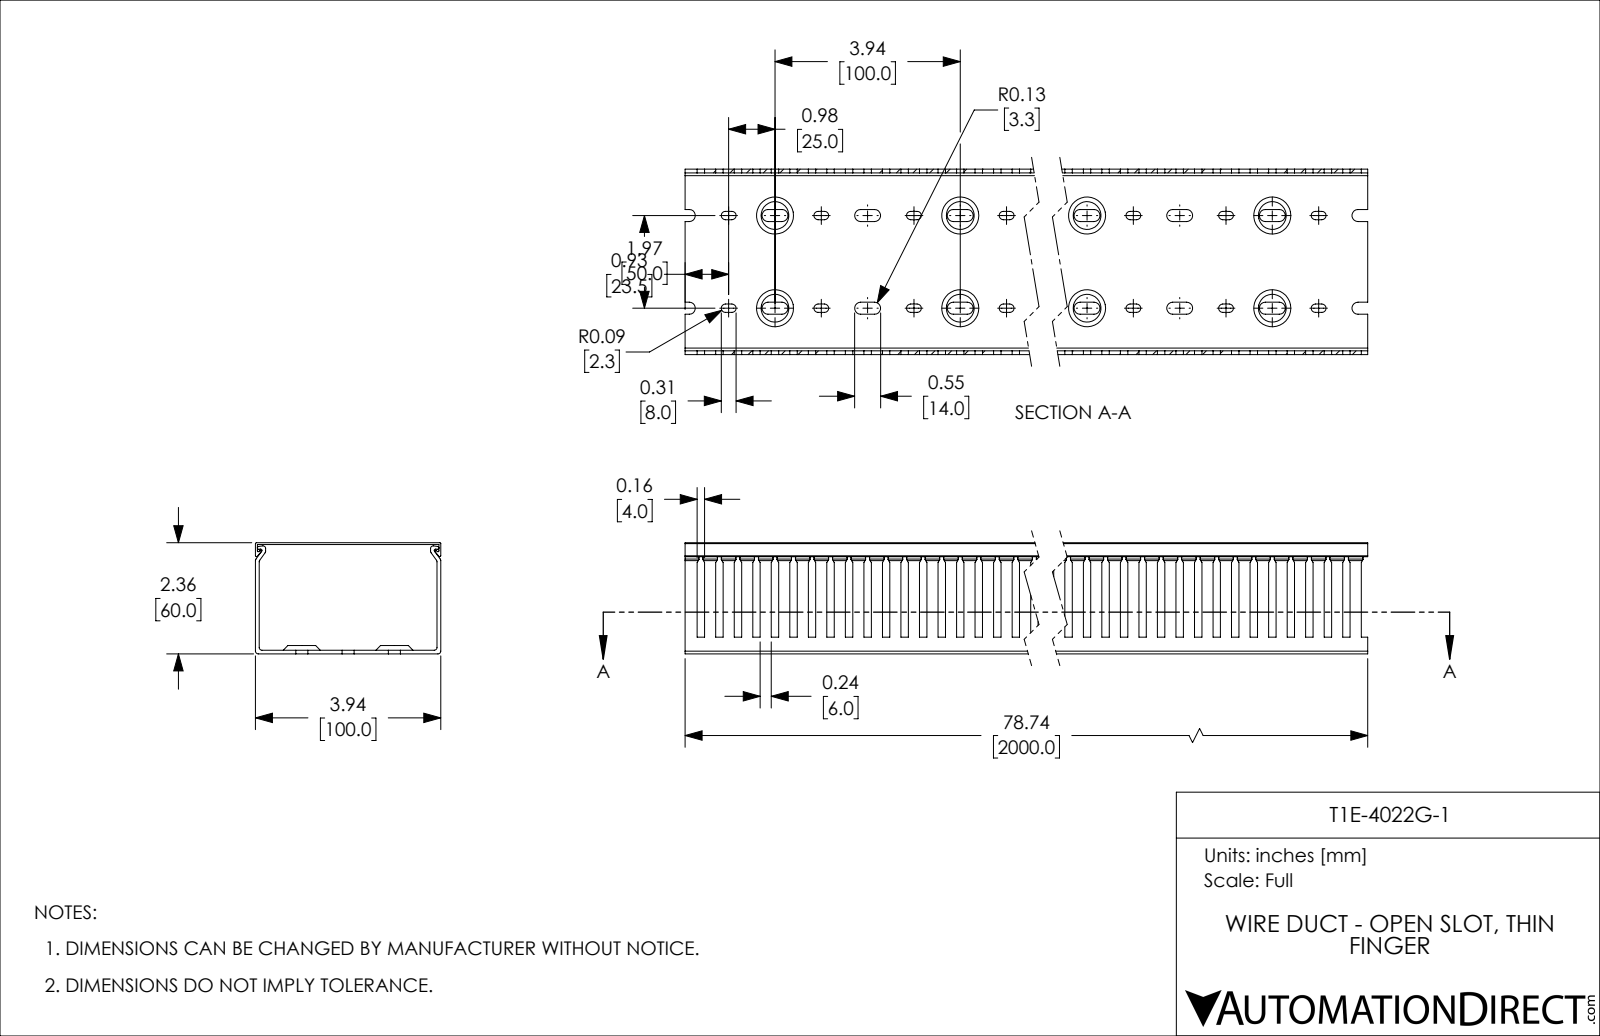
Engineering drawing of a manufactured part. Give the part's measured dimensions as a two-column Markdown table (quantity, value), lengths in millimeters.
| quantity | value |
| --- | --- |
| part name | T1E-4022G-1 |
| STEP written by | SolidWorks 2021 (CONFIG_CONTROL_DESIGN) |
| units | millimeters |
| bodies | 2 solids, 1573 faces (762 planar, 731 cylindrical, 80 other) |
| overall size | 2000 × 100 × 60 |
| volume | 1 097 000 mm³ |
| surface area | 1 335 000 mm² |
| partial cylindrical surfaces (radius × count) | 3.25 × 200, 2.25 × 160, 1.5 × 12, 0.5 × 8, 0.75 × 6 |
| main face-to-face distances | 2, 1, 98, 60, 59, 57, 58, 100, 96, 99 |
